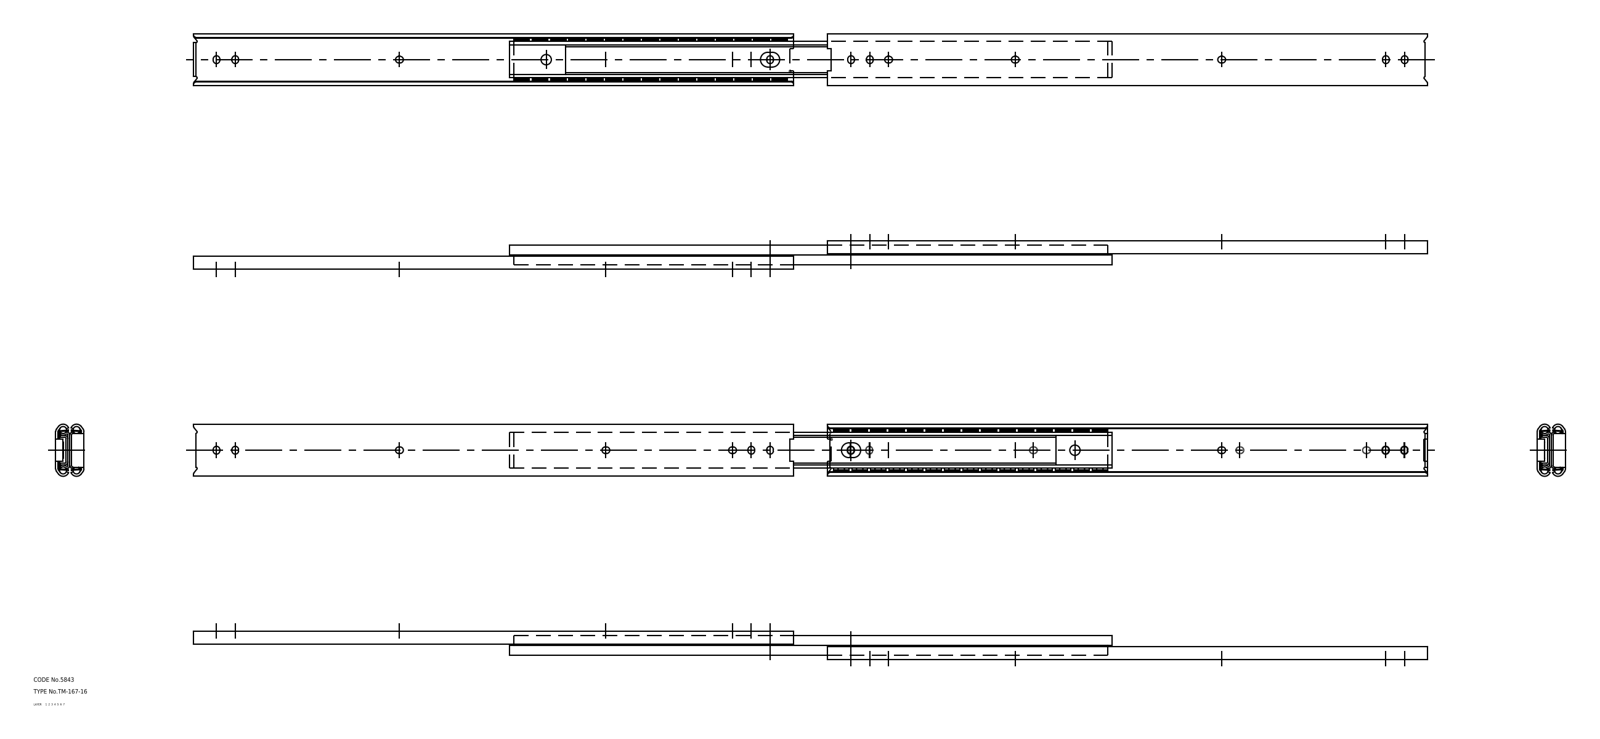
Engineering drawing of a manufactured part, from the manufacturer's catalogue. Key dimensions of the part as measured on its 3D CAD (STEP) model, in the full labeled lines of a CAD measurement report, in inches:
Part name (STEP PRODUCT): member_A_mr-1; ball; retainer_mr-1; member_B_mr-1 (+4 more)
STEP written by: CADfix (AUTOMOTIVE_DESIGN)
Units: inches
Bodies: 66 solids, 888 faces (0 planar, 0 cylindrical, 888 other)
Overall size (bounding box): 32.874 × 1.39 × 0.752
Volume: 7.583 in³ · Surface area: 285.6 in²
